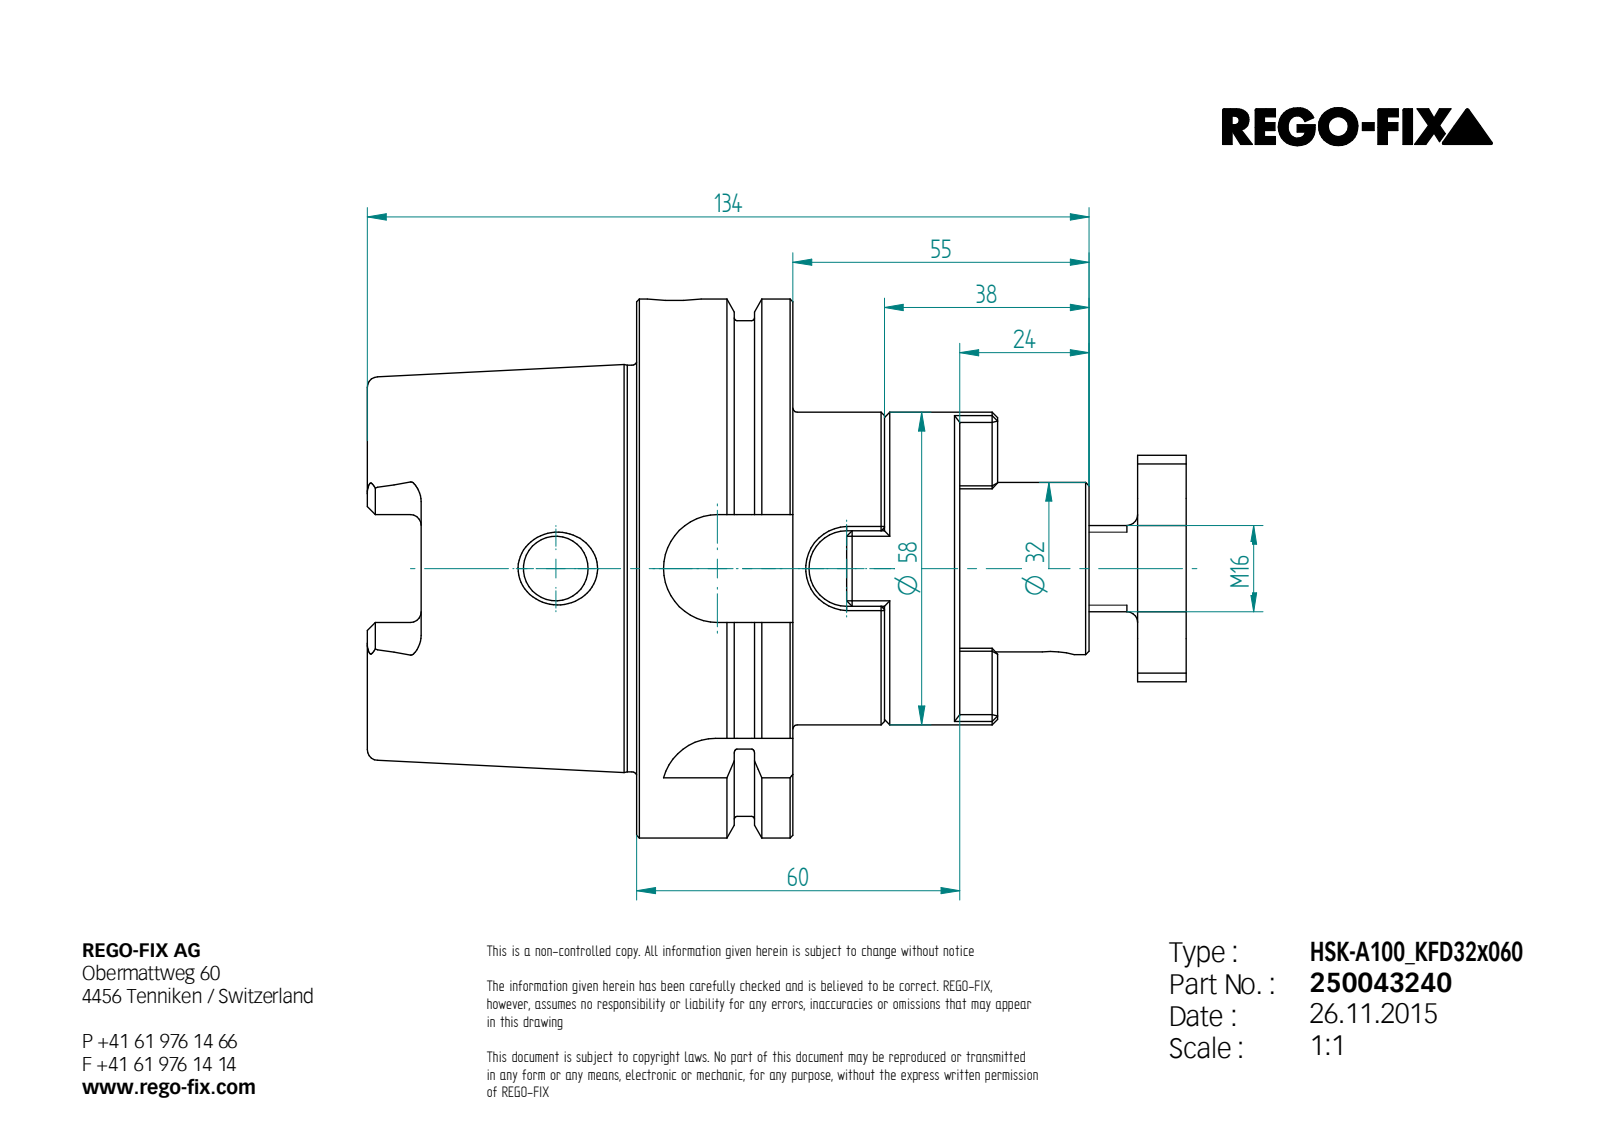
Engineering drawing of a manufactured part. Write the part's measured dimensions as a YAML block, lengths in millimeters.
step_written_by: "Unknown (AUTOMOTIVE_DESIGN)"
units: millimeters
bodies: {solids: 3, faces: 255, planar: 125, cylindrical: 52, other: 78}
overall_size: [152, 100, 100]
volume: 361109
surface_area: 72629
round_holes:
  - {diameter: 12, count: 2}
  - {diameter: 8.5, count: 1}
  - {diameter: 10, count: 1}
  - {diameter: 13.84, count: 1}
  - {diameter: 17, count: 1}
  - {diameter: 22.38, count: 1}
  - {diameter: 25, count: 1}
  - {diameter: 32, count: 1}
  - {diameter: 53, count: 1}
  - {diameter: 63, count: 1}
round_bosses_or_shafts:
  - {diameter: 100, count: 1}
  - {diameter: 92, count: 1}
  - {diameter: 75.46, count: 1}
  - {diameter: 58, count: 1}
  - {diameter: 31.4, count: 1}
  - {diameter: 16, count: 1}
partial_cylinders:
  - {radius: 2, count: 6}
  - {radius: 4.88, count: 4}
  - {radius: 5, count: 4}
  - {radius: 4, count: 2}
  - {radius: 10, count: 2}
  - {radius: 7, count: 1}
  - {radius: 11, count: 1}
  - {radius: 21, count: 1}
face_to_face_distances: [17, 29, 46, 12.5, 14, 16.5, 33.5, 47.5, 102, 60]
